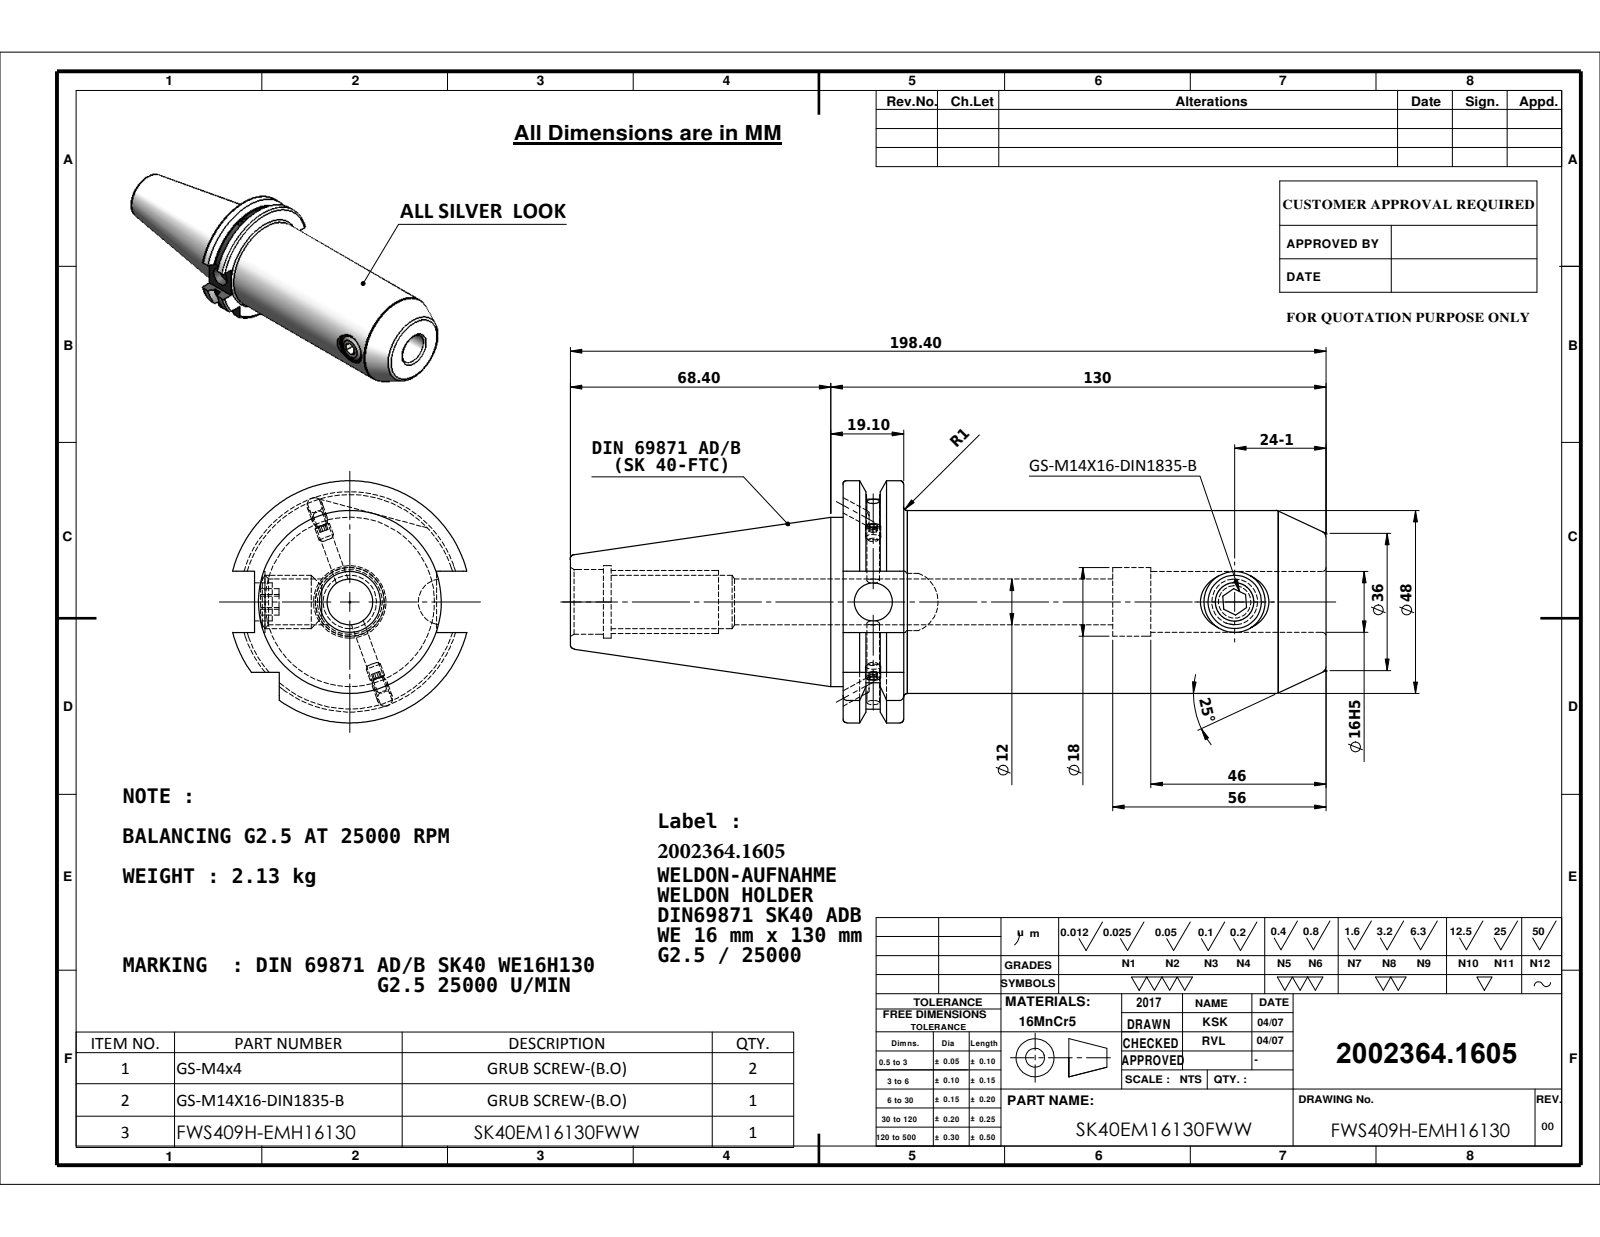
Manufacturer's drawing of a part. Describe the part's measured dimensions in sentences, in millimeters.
The part is named "91406-WE716130; SK40EM16130FWW; Copy of M4X4_DIN 913 - M4 x 4-N; M14X16_ISO 4026 - M12 x 12-N". Its 3-D file was written by "SolidWorks 2009 (CONFIG_CONTROL_DESIGN)". It is 4 solids with 161 faces: 59 planar, 45 cylindrical and 57 other. Overall it measures 198.4 by 63.55 by 61.48 millimeters. Its volume is 277 140 cubic millimeters and its surface area 43 518 square millimeters. Round holes: 2 of diameter 12, 2 of diameter 16, 1 of diameter 3.3, 1 of diameter 10, 1 of diameter 14, 1 of diameter 17, 1 of diameter 18, 1 of diameter 19. Round bosses or shafts: 2 of diameter 4, 1 of diameter 48, 1 of diameter 44.45, 1 of diameter 14. Partial cylindrical surfaces (rounded edges, fillets, slot ends): 1 of radius 8.05, 1 of radius 28.12, 1 of radius 31.77. The main face-to-face distances are 15.9, 126.8, 110.9, 16.1, 47.8, 70.8, 54.9, 56, 71.6, 87.5. The hole center spacings are 94.85.
